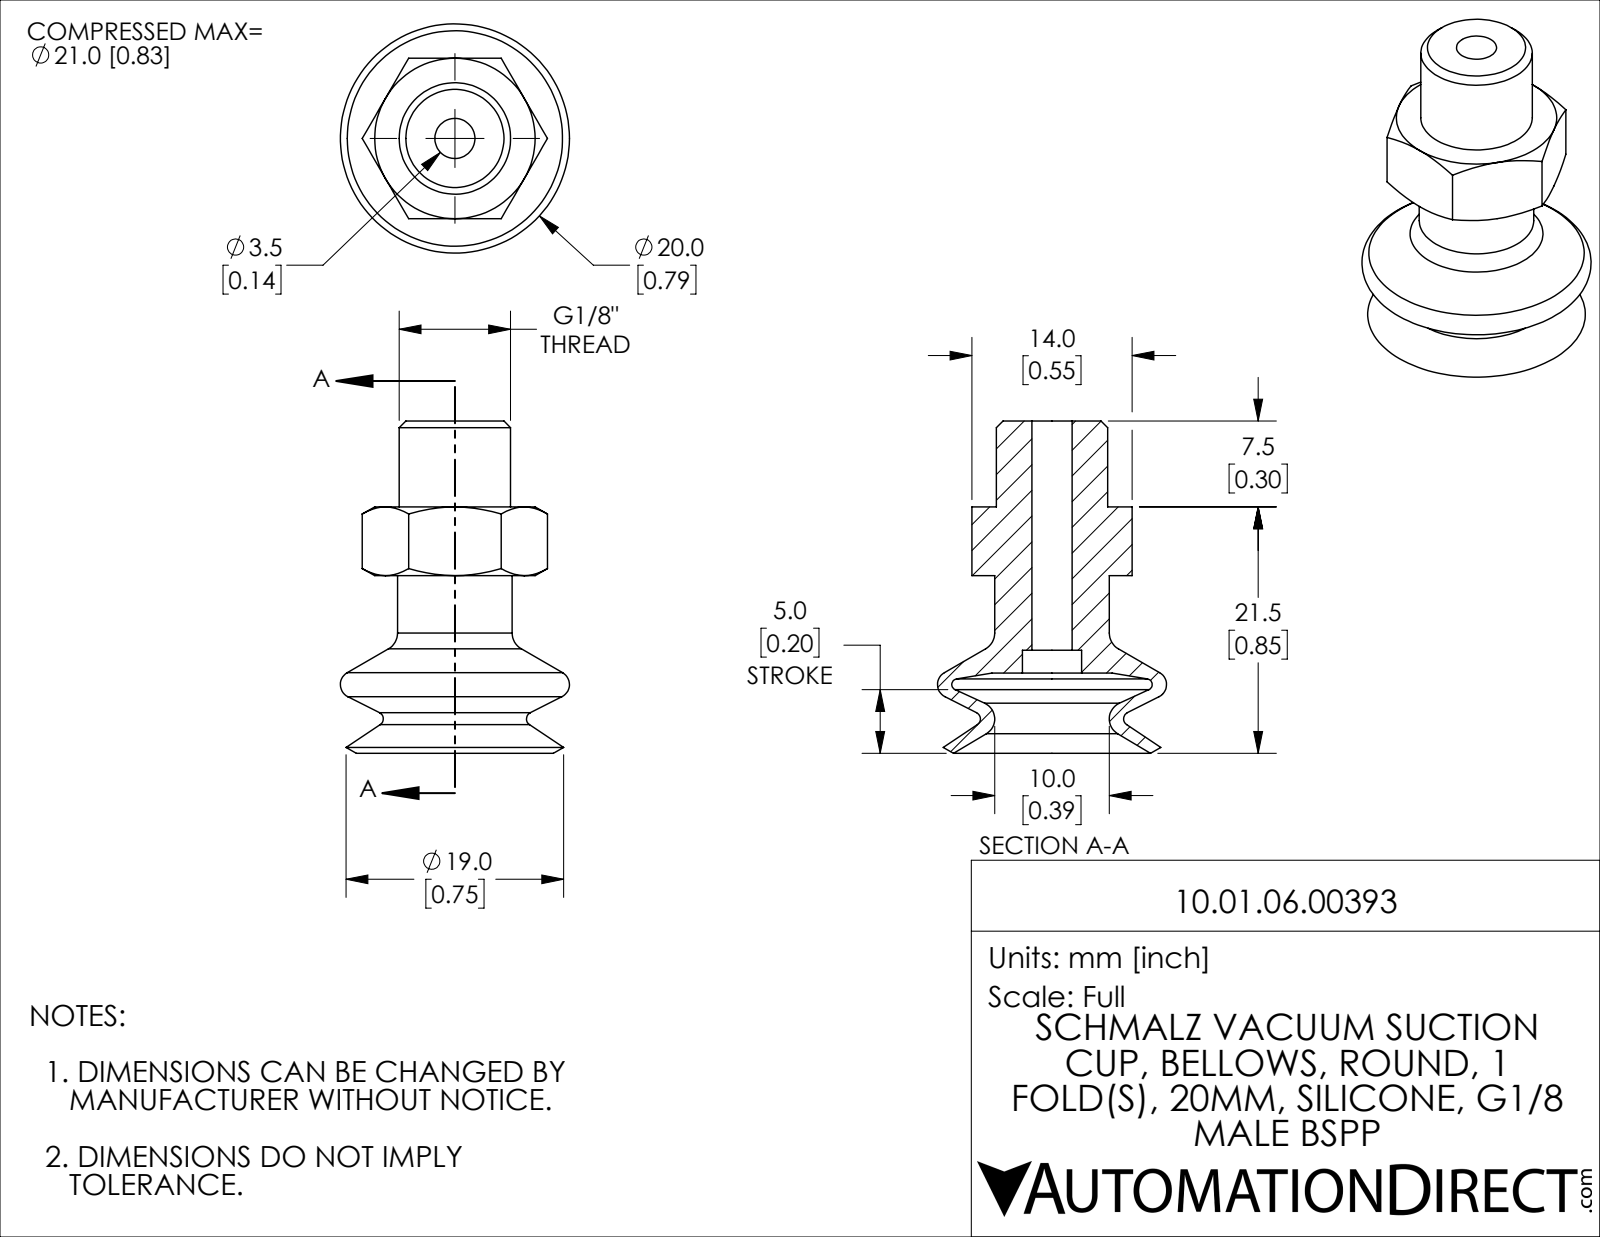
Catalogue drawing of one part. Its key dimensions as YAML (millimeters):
part_name: "10.01.06.00393"
step_written_by: "SolidWorks 2021 (CONFIG_CONTROL_DESIGN)"
units: millimeters
bodies: {solids: 1, faces: 63, planar: 11, cylindrical: 8, other: 44}
overall_size: [29, 20, 20]
volume: 2814
surface_area: 2676
round_holes:
  - {diameter: 3.5, count: 1}
  - {diameter: 5.16, count: 1}
round_bosses_or_shafts:
  - {diameter: 10, count: 1}
  - {diameter: 9.73, count: 1}
face_to_face_distances: [14, 6, 8.5, 14.5, 22, 13.5, 7.5, 2, 6.5, 12.5]
